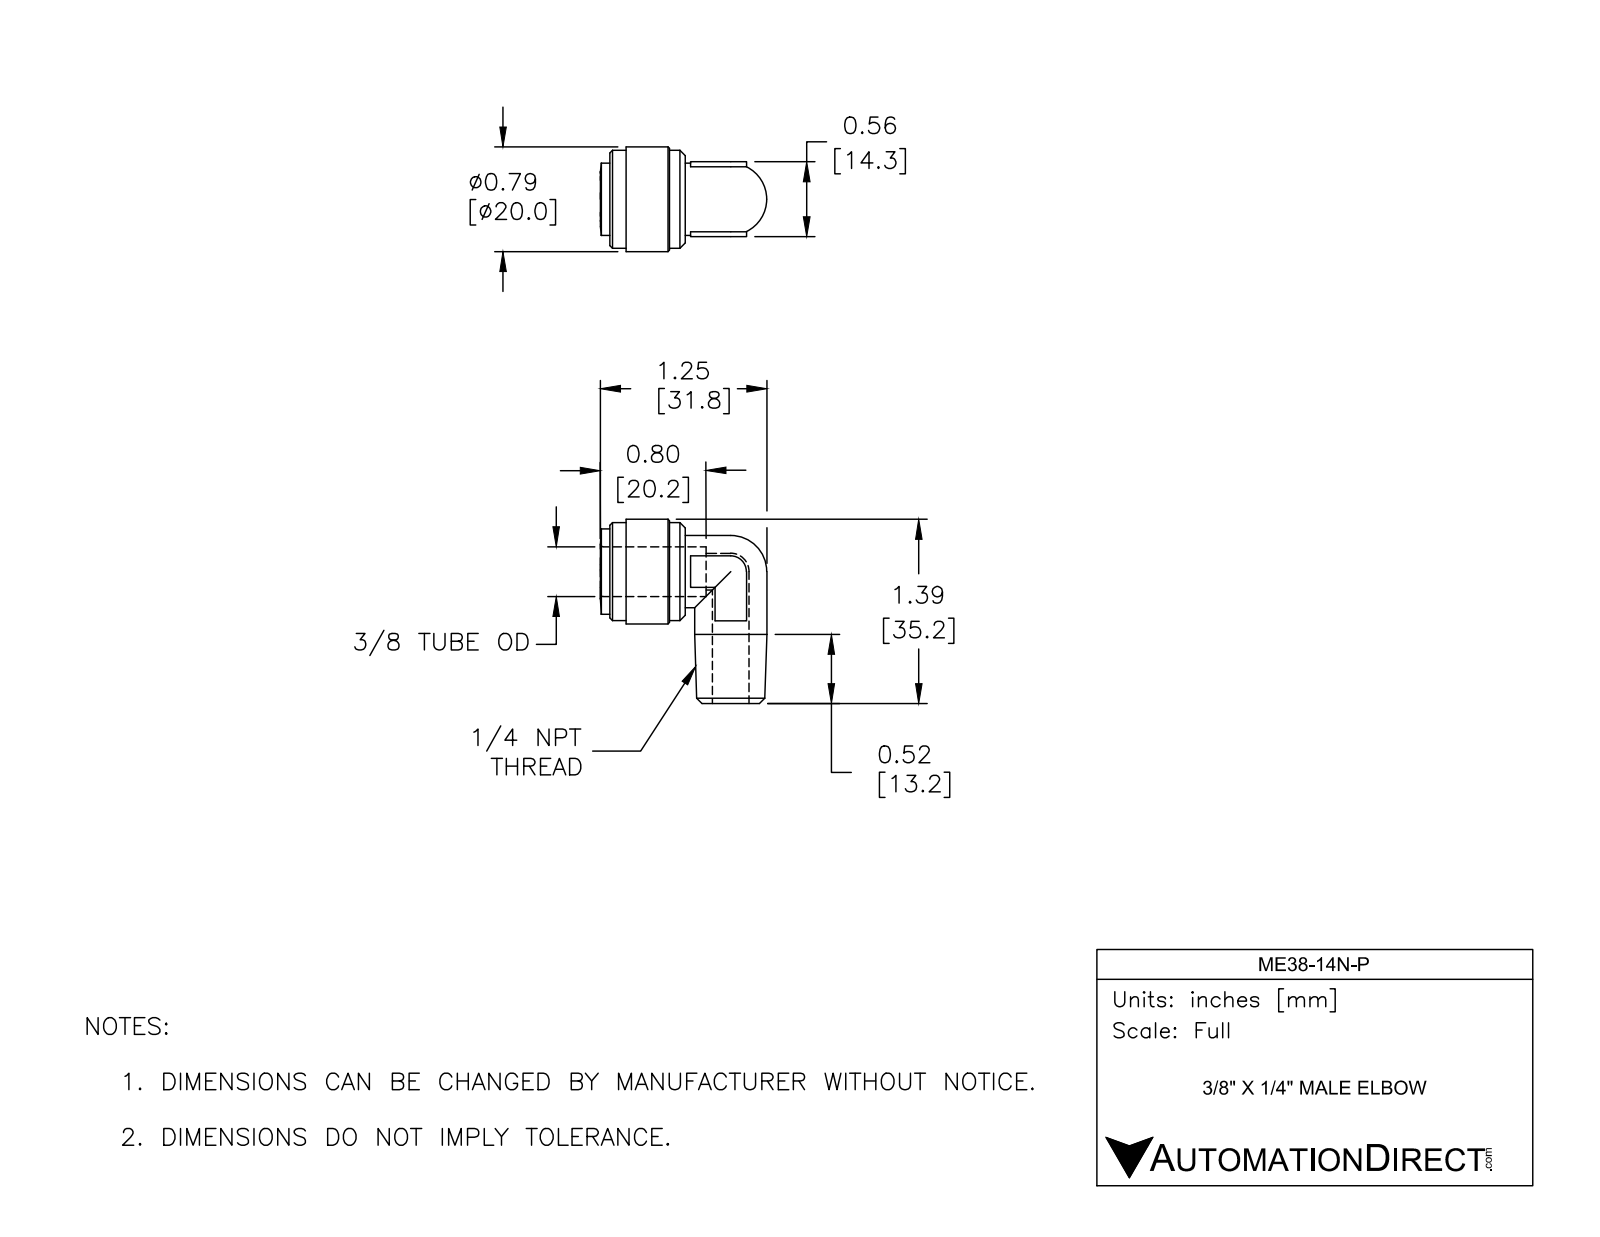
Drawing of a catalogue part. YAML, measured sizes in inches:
part_name: "ME38-14N-P"
step_written_by: "SolidWorks 2017 (AUTOMOTIVE_DESIGN)"
units: inches
bodies: {solids: 1, faces: 58, planar: 20, cylindrical: 18, other: 20}
overall_size: [1.386, 1.252, 0.787]
volume: 0.422
surface_area: 6.393
round_holes:
  - {diameter: 0.276, count: 2}
  - {diameter: 0.374, count: 1}
round_bosses_or_shafts:
  - {diameter: 0.543, count: 2}
  - {diameter: 0.787, count: 1}
  - {diameter: 0.736, count: 1}
partial_cylinders:
  - {radius: 0.118, count: 1}
face_to_face_distances: [0.563, 0.567, 0.122, 0.445, 0.157, 0.724, 0.602, 0.118, 0.449, 0.327]
